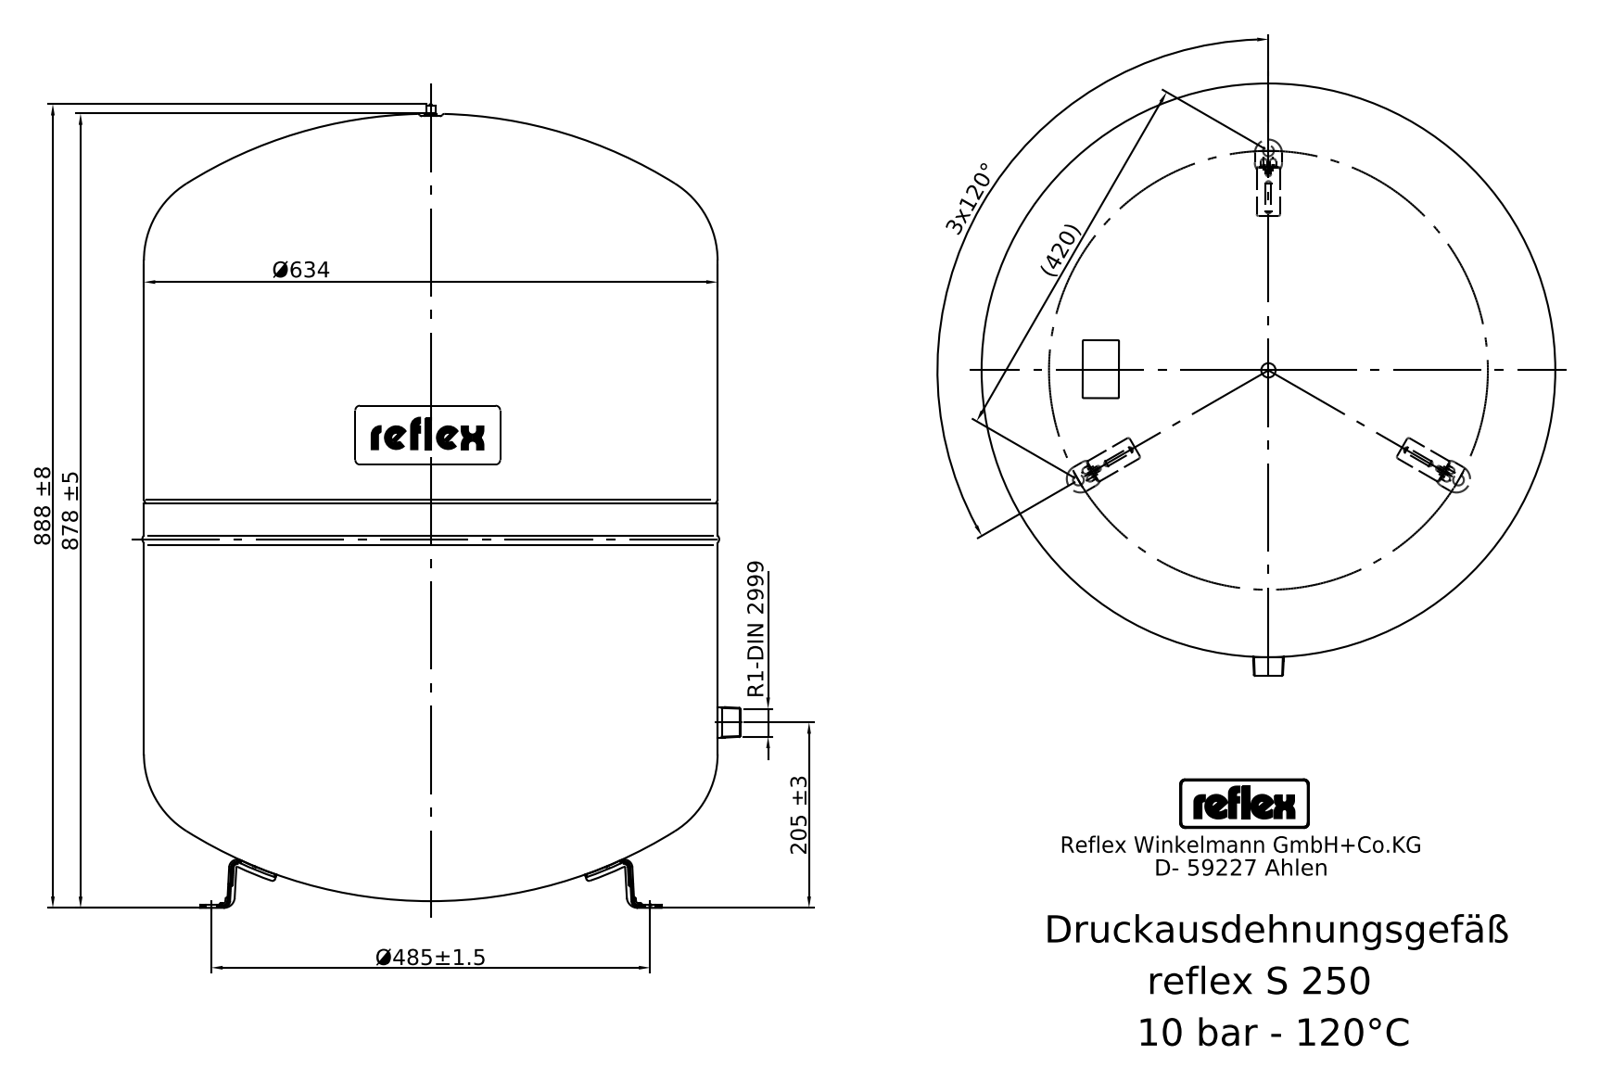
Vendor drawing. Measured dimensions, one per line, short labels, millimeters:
written by: Mechanical Desktop 2011 (CONFIG_CONTROL_DESIGN)
unit: mm
bodies: 16 solids, 208 faces (79 planar, 76 cylindrical, 53 other)
size: 889.5 × 663.4 × 642.8
volume: 239 600 000 mm³; area: 3 284 000 mm²
holes: 3× ⌀15, 1× ⌀5.64
bosses: 1× ⌀634, 1× ⌀33.7, 1× ⌀6.84, 1× ⌀3.6, 1× ⌀2.4
rounds: 9× R148.38, 9× R150.38, 6× R15, 4× R3.94, 3× R1.57, 2× R2.69, 2× R4.72, 2× R6.49
face distances: 546, 273, 3.15, 168, 441, 714, 2, 170, 443, 716
hole spacings: 242.5, 420.02
